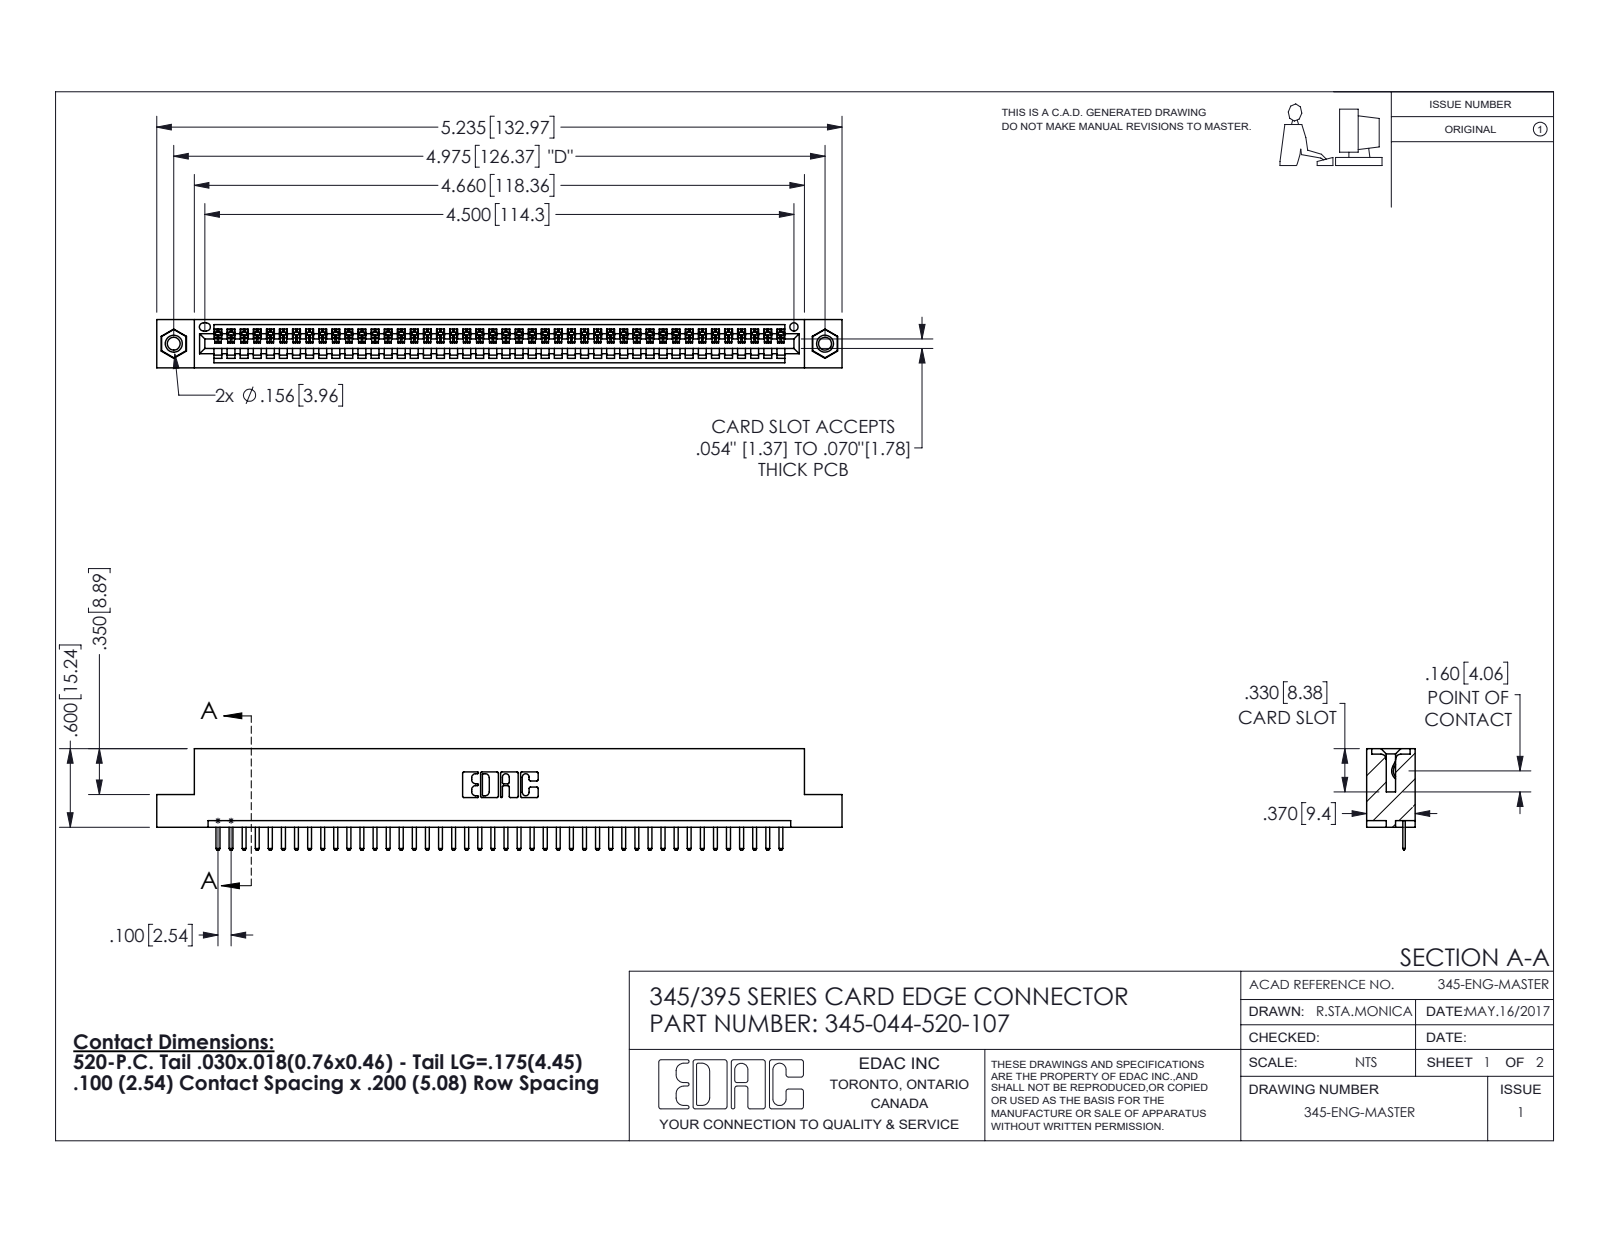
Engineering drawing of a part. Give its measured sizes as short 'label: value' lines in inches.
name: 345-250-001_345-250-005-103; 345-044-520-107; 345-292-001_345-293-120; 345 Part_Flush Mounting Lugs - 0.156 Dia-TI
written by: SolidWorks 2016 (CONFIG_CONTROL_DESIGN)
unit: in
bodies: 47 solids, 2914 faces (1960 planar, 938 cylindrical, 16 other)
size: 5.235 × 0.775 × 0.37
volume: 0.763 in³; area: 25.21 in²
holes: 2× ⌀0.098, 2× ⌀0.125, 2× ⌀0.156, 1× ⌀0.064
bosses: 2× ⌀0.155
rounds: 90× R0.01, 88× R0.006, 22× R0.01, 6× R0.007, 6× R0.031, 3× R0.026, 2× R0.031, 2× R0.04
face distances: 0.072, 0.298, 0.37, 0.2, 0.098, 0.272, 0.025, 0.225, 0.072, 0.149
hole spacings: 0.27, 4.739, 4.975
